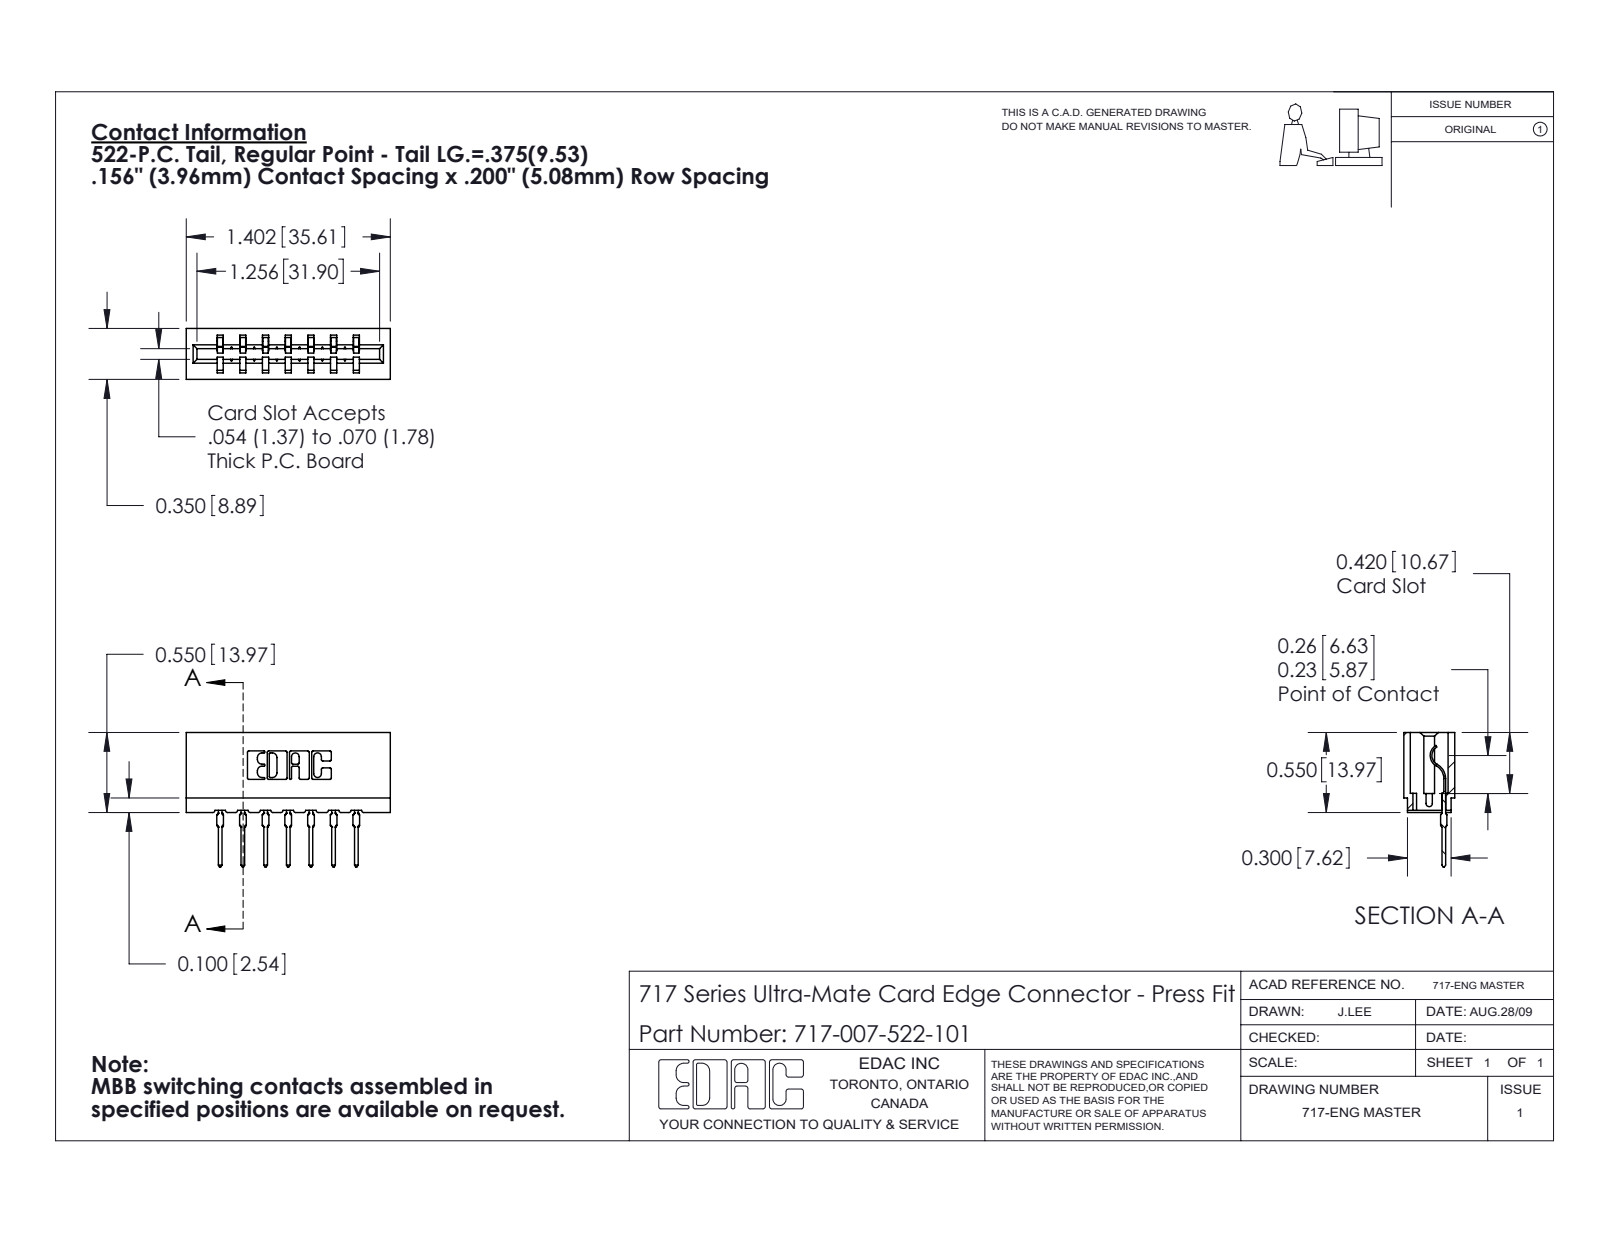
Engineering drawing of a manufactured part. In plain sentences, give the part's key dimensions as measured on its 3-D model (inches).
The part is named "745-292-001_522; 717 Part_Insulator Option - 06; 717-007-522-101". Its 3-D file was written by "SolidWorks 2020 (CONFIG_CONTROL_DESIGN)". It is 8 solids with 885 faces: 530 planar, 173 cylindrical and 182 other. Overall it measures 1.402 by 0.924 by 0.35 inches. Its volume is 0.193 cubic inches and its surface area 6.334 square inches. Partial cylindrical surfaces (rounded edges, fillets, slot ends): 22 of radius 0.01, 14 of radius 0.015, 14 of radius 0.021, 6 of radius 0.007, 6 of radius 0.031, 4 of radius 0.005, 4 of radius 0.011, 3 of radius 0.026. The main face-to-face distances are 0.212, 0.156, 0.138, 0.35, 0.198, 0.312, 0.468, 0.624, 0.042, 0.27.
